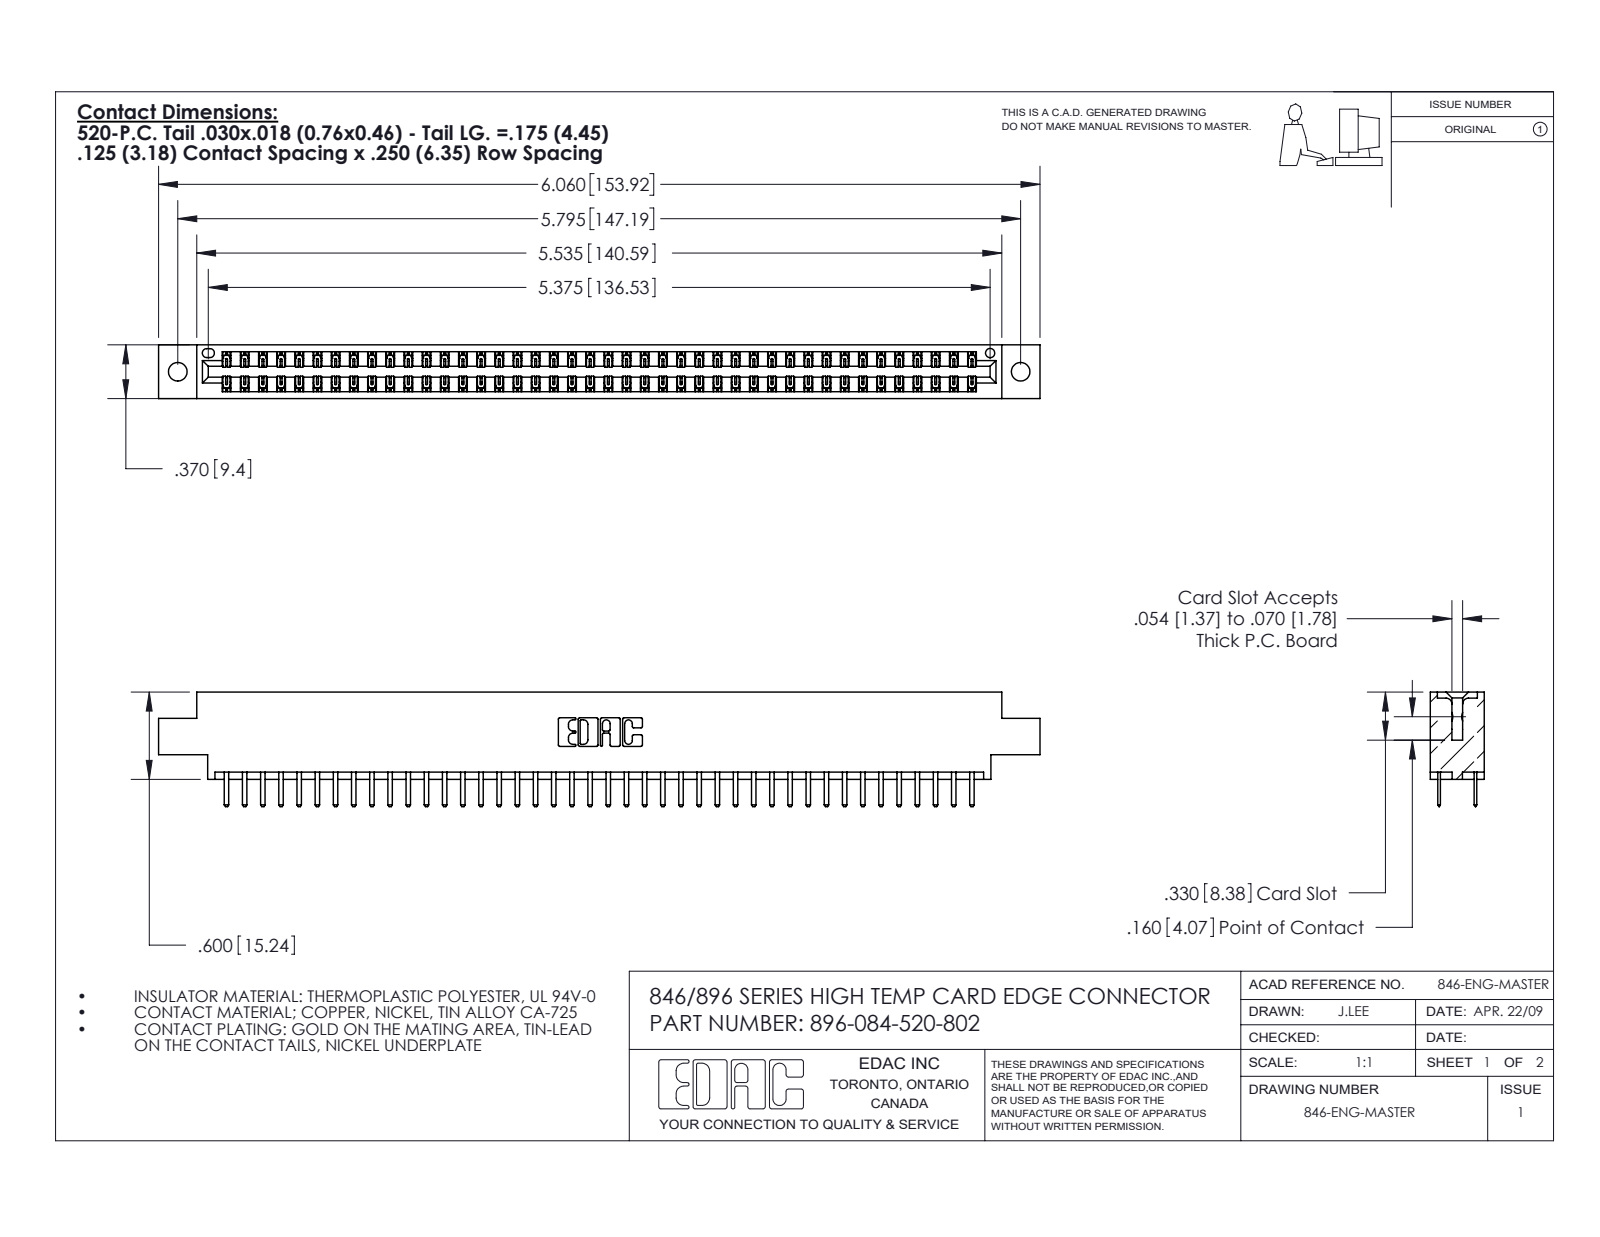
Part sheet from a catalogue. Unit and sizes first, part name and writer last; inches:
Units: inches
Overall size (bounding box): 6.06 × 0.788 × 0.37
Round holes (diameter × count): ⌀0.128 ×2, ⌀0.064 ×1
Partial cylindrical surfaces — rounded edges, fillets, slot ends (radius × count): R0.006 ×126, R0.01 ×88, R0.01 ×22, R0.007 ×6, R0.031 ×6, R0.026 ×3, R0.014 ×2, R0.022 ×2
Main face-to-face distances: 0.048, 0.322, 0.25, 0.37, 0.275, 0.072, 0.298, 0.025, 0.148, 0.222
Hole centre spacings: 0.246, 5.586, 5.795
Volume: 0.902 in³ · Surface area: 31.22 in²
Bodies: 85 solids, 4830 faces (3188 planar, 1642 cylindrical, 0 other)
Part name (STEP PRODUCT): 345-292-001_345-293-120; 396-084-520-802; 346 Part_0.170 Offset - 0.128 Dia
STEP written by: SolidWorks 2016 (CONFIG_CONTROL_DESIGN)
